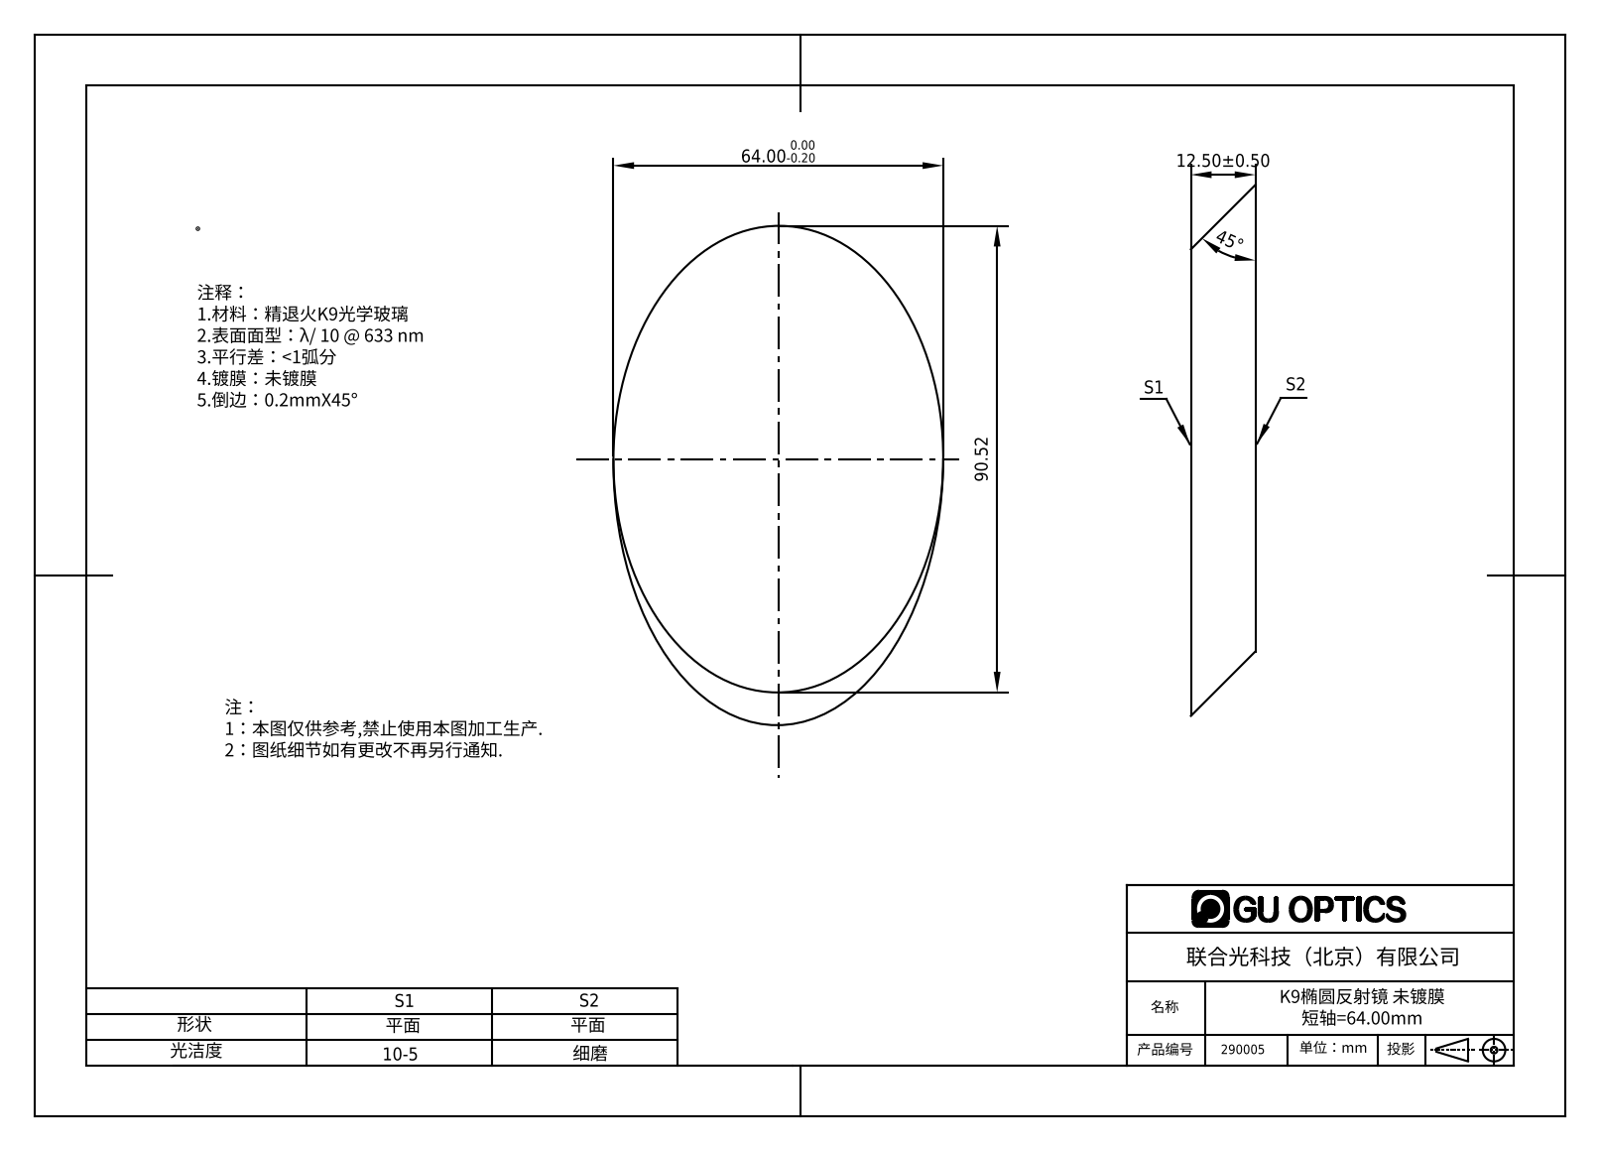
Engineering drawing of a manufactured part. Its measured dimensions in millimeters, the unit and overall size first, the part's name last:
Units: millimetres
Overall size (bounding box): 103.02 × 64 × 12.5
Main face-to-face distances: 12.5
Volume: 56 880 mm³ · Surface area: 12 653 mm²
Bodies: 1 solid, 4 faces (2 planar, 0 cylindrical, 2 other)
Part name (STEP PRODUCT): 290005
STEP written by: SolidWorks 2016 (AUTOMOTIVE_DESIGN)
